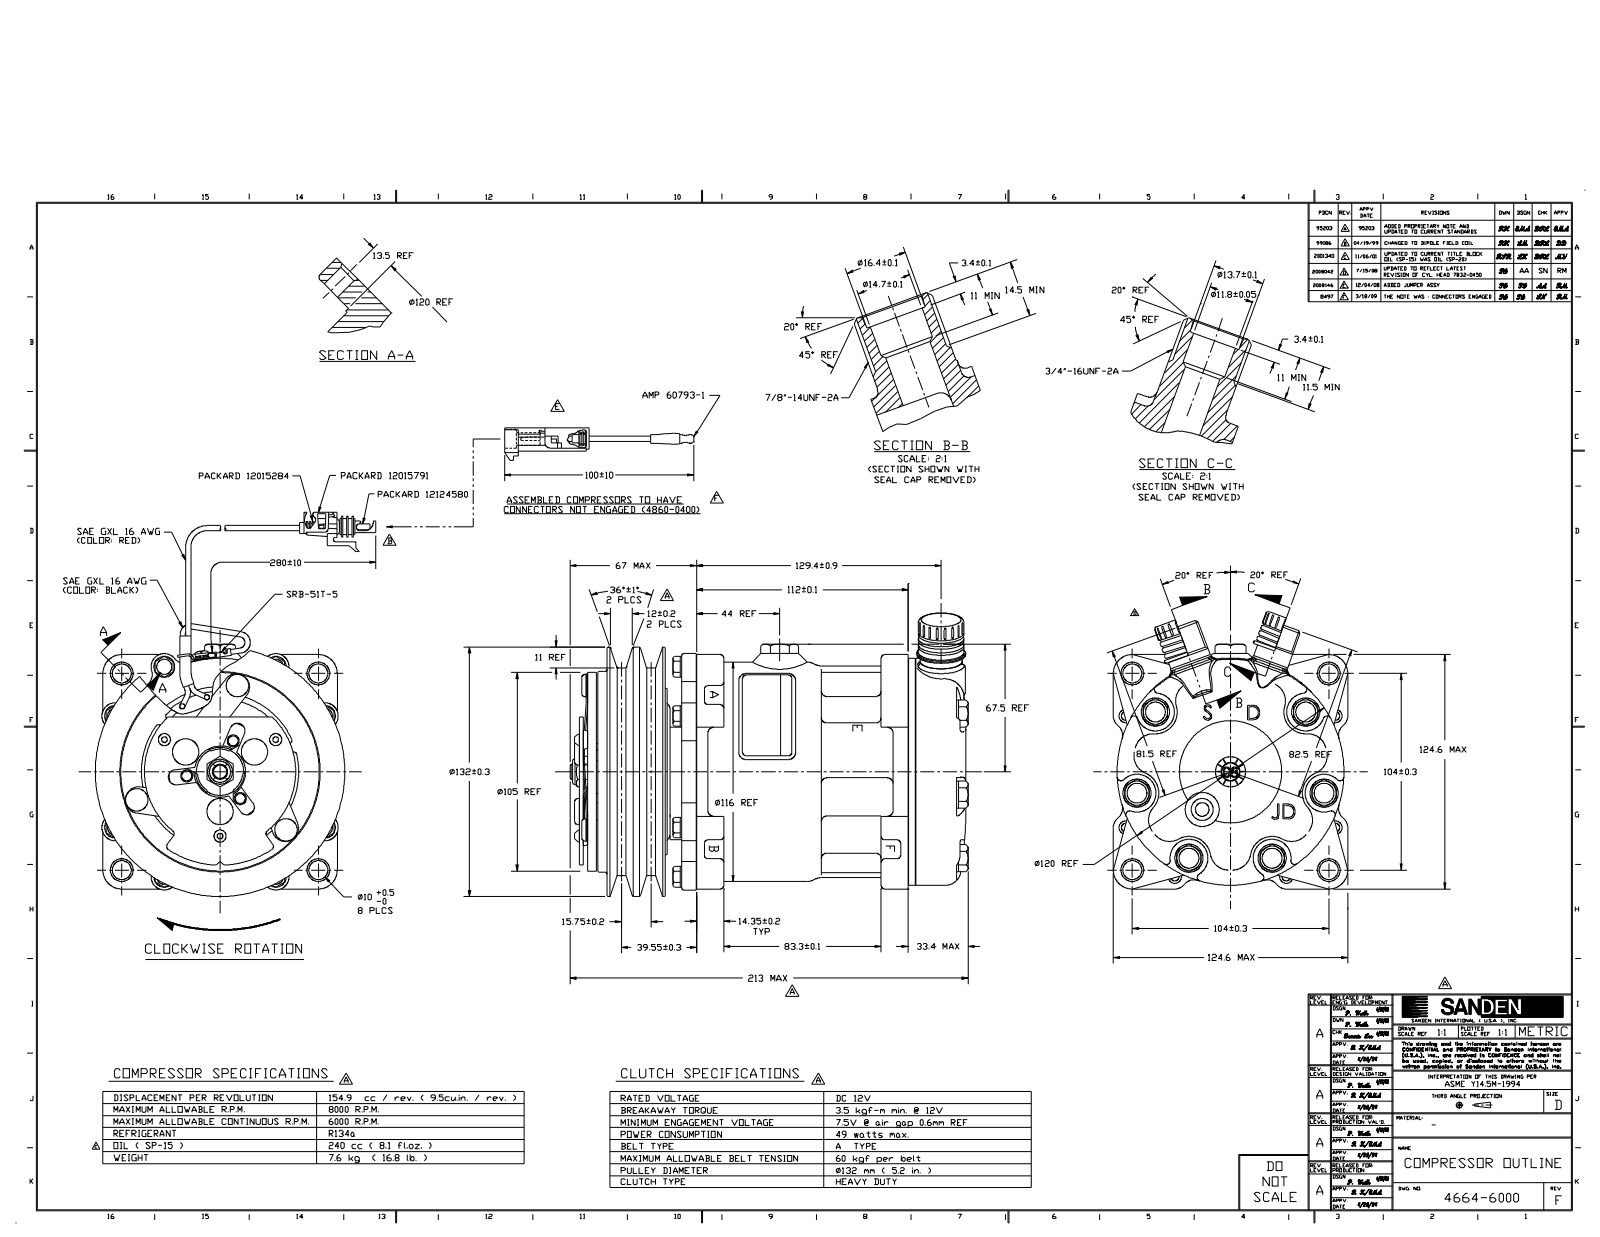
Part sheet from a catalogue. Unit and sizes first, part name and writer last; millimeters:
Units: millimetres
Overall size (bounding box): 488.42 × 210.54 × 132
Round holes (diameter × count): ⌀5.5 ×8, ⌀7 ×8, ⌀8.5 ×8, ⌀8 ×6, ⌀11.9 ×6, ⌀10.25 ×4, ⌀5.1 ×3, ⌀6.35 ×3, ⌀7.5 ×3, ⌀3.5 ×1, ⌀4 ×1, ⌀5 ×1
Round bosses / shafts (diameter × count): ⌀12.9 ×8, ⌀5.69 ×8, ⌀15.3 ×6, ⌀2.7 ×5, ⌀18 ×3, ⌀16 ×3, ⌀11 ×3, ⌀9 ×3
Partial cylindrical surfaces — rounded edges, fillets, slot ends (radius × count): R2 ×33, R1 ×28, R6.5 ×25, R1.5 ×24, R7 ×24, R3 ×19, R5 ×19, R0.5 ×14
Main face-to-face distances: 2, 44.84, 44.95, 49.75, 4.8, 0.6, 45.55, 4.2, 39.46, 5.49
Hole centre spacings: 62.85, 22.77, 81.58, 88.89, 109.83, 134.9, 42.09, 16
Volume: 2 094 000 mm³ · Surface area: 249 440 mm²
Bodies: 1 solid, 2400 faces (675 planar, 705 cylindrical, 1020 other)
Part name (STEP PRODUCT): SANDEN_4664_REV_F_COMPR_AC
STEP written by: SolidWorks 2010 (CONFIG_CONTROL_DESIGN)
